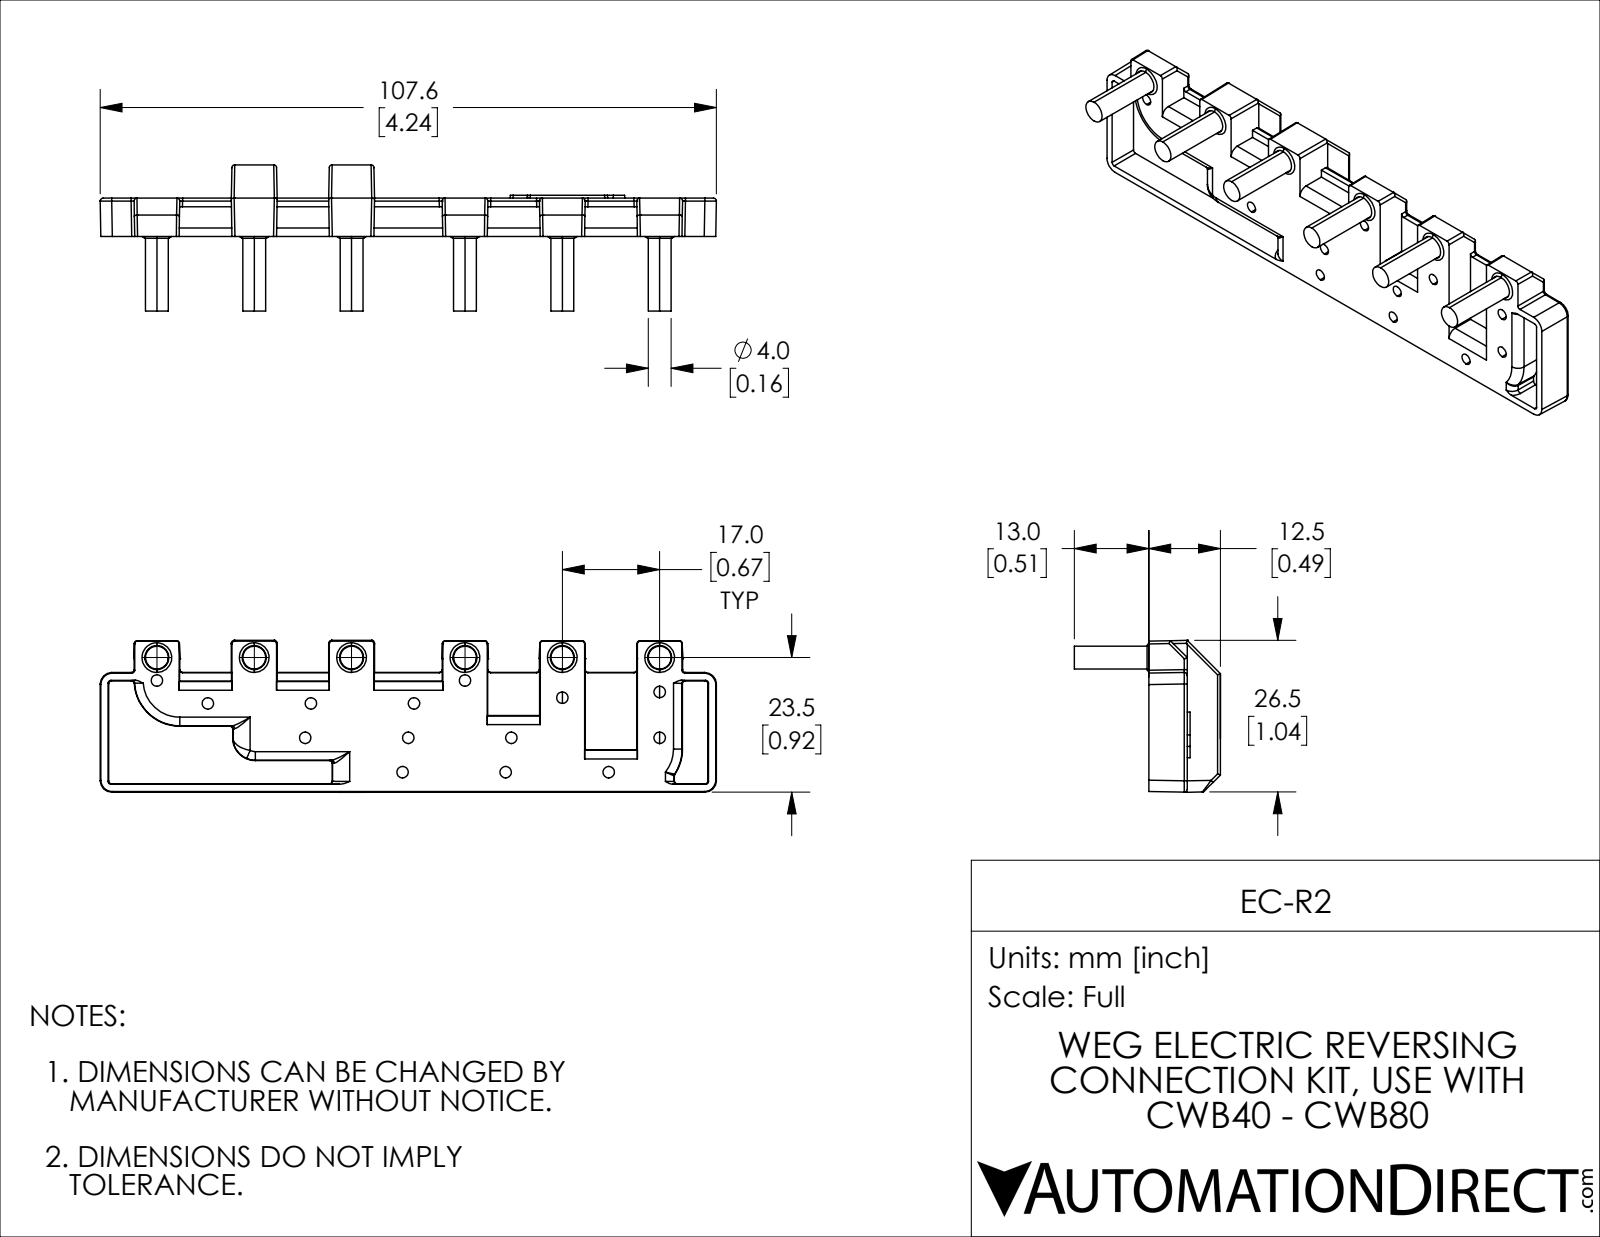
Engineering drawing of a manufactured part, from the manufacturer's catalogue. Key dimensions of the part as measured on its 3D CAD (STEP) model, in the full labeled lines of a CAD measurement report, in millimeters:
Part name (STEP PRODUCT): EC-R2
STEP written by: SolidWorks 2019 (CONFIG_CONTROL_DESIGN)
Units: millimetres
Bodies: 4 solids, 460 faces (163 planar, 156 cylindrical, 141 other)
Overall size (bounding box): 107.6 × 26.5 × 25.5
Volume: 18 910 mm³ · Surface area: 13 420 mm²
Partial cylindrical surfaces — rounded edges, fillets, slot ends (radius × count): R0.5 ×56, R2 ×25, R1 ×14, R0.8 ×10, R1.5 ×7, R2.1 ×6, R3 ×2
Main face-to-face distances: 6.7, 5.2, 1.5, 17, 25, 2, 53.8, 5.8, 7.3, 12.5
